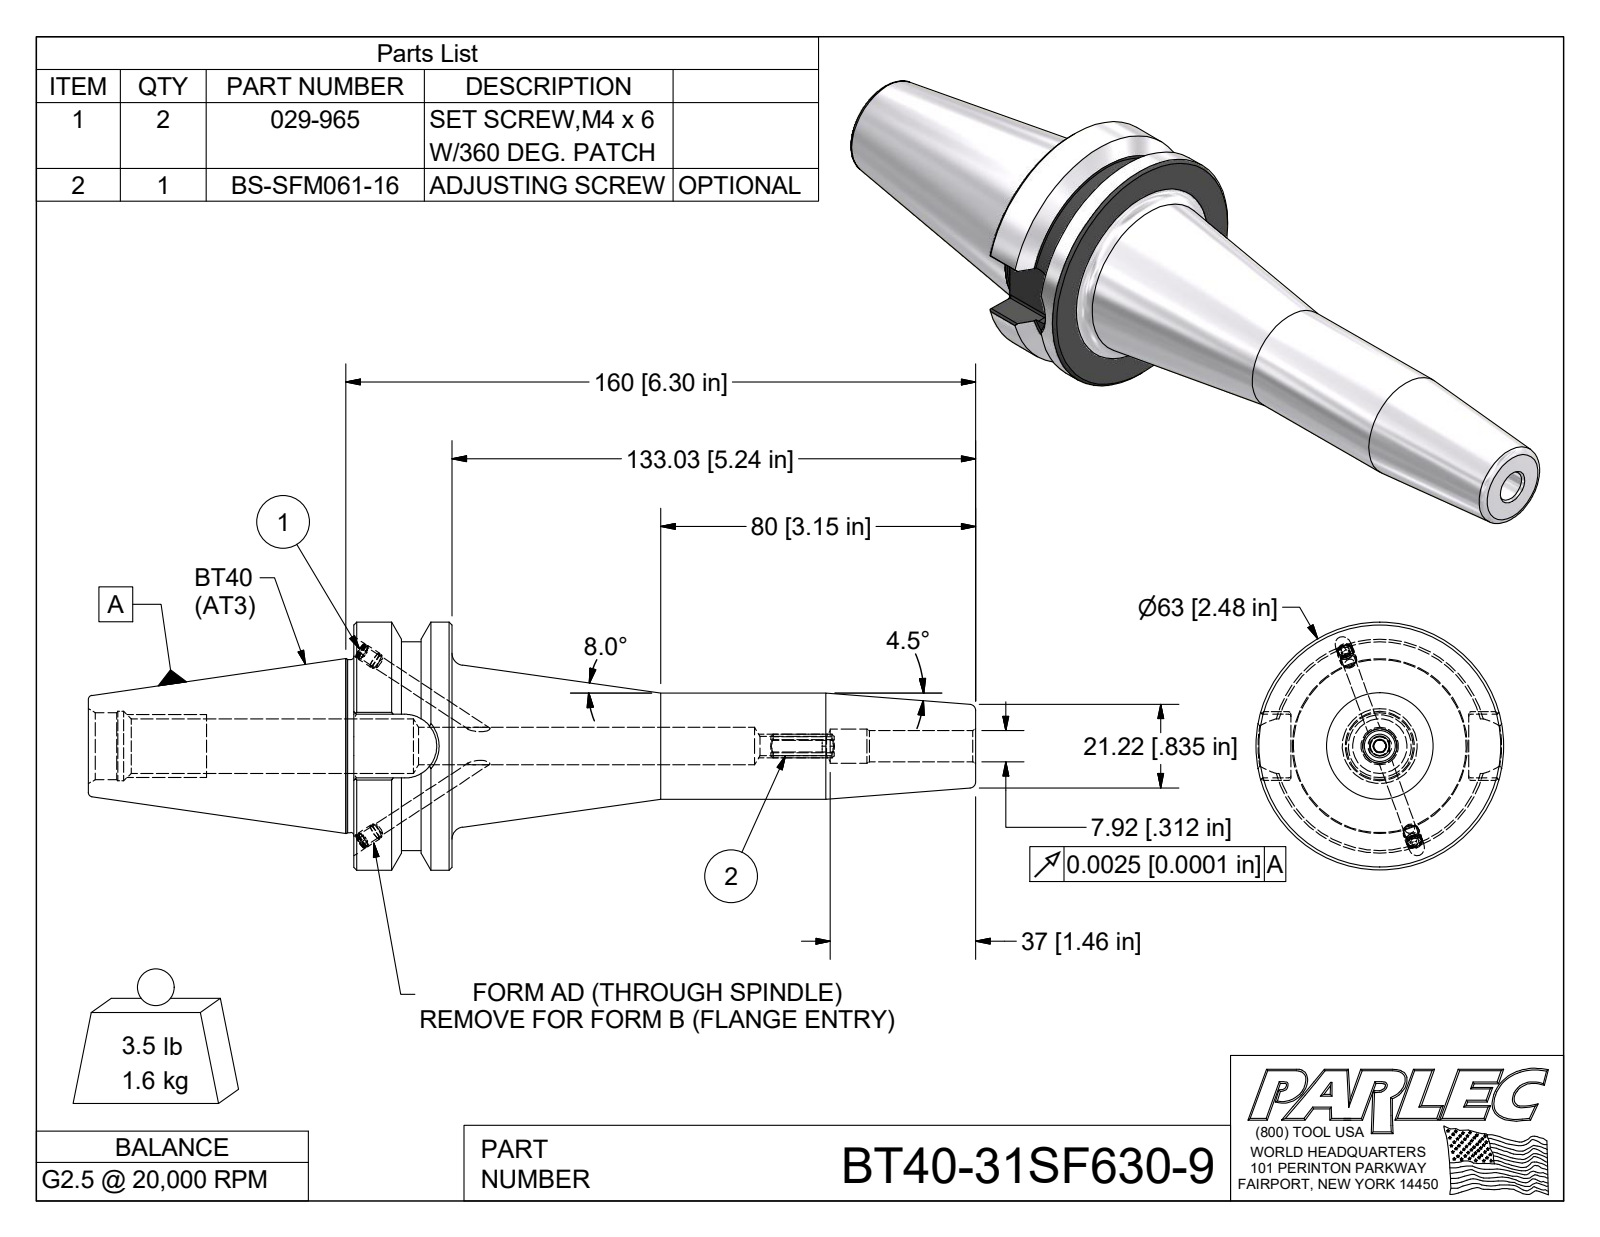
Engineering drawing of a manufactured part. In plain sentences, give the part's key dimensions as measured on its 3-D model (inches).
The part is named "BT40-31SF630-9; BT40BC-31SF630-9-1; 029-965; BS-SFM061-16". Its 3-D file was written by "Autodesk Inventor 2009 (AUTOMOTIVE_DESIGN)". It is 4 solids with 139 faces: 57 planar, 33 cylindrical and 49 other. Overall it measures 8.874 by 2.48 by 2.48 inches. Its volume is 12.43 cubic inches and its surface area 59.54 square inches. Round holes: 2 of diameter 0.13, 2 of diameter 0.161, 1 of diameter 0.312, 1 of diameter 0.342, 1 of diameter 0.694. Round bosses or shafts: 2 of diameter 0.165, 2 of diameter 0.157, 1 of diameter 2.48, 1 of diameter 2.087, 1 of diameter 1.75, 1 of diameter 1.73, 1 of diameter 1.063. Partial cylindrical surfaces (rounded edges, fillets, slot ends): 8 of radius 0.02, 1 of radius 0.118, 1 of radius 0.319. The main face-to-face distances are 0.984, 1.78, 6.221, 5.237, 2.653, 3.637, 8.874, 0.637, 0.197, 0.792.
